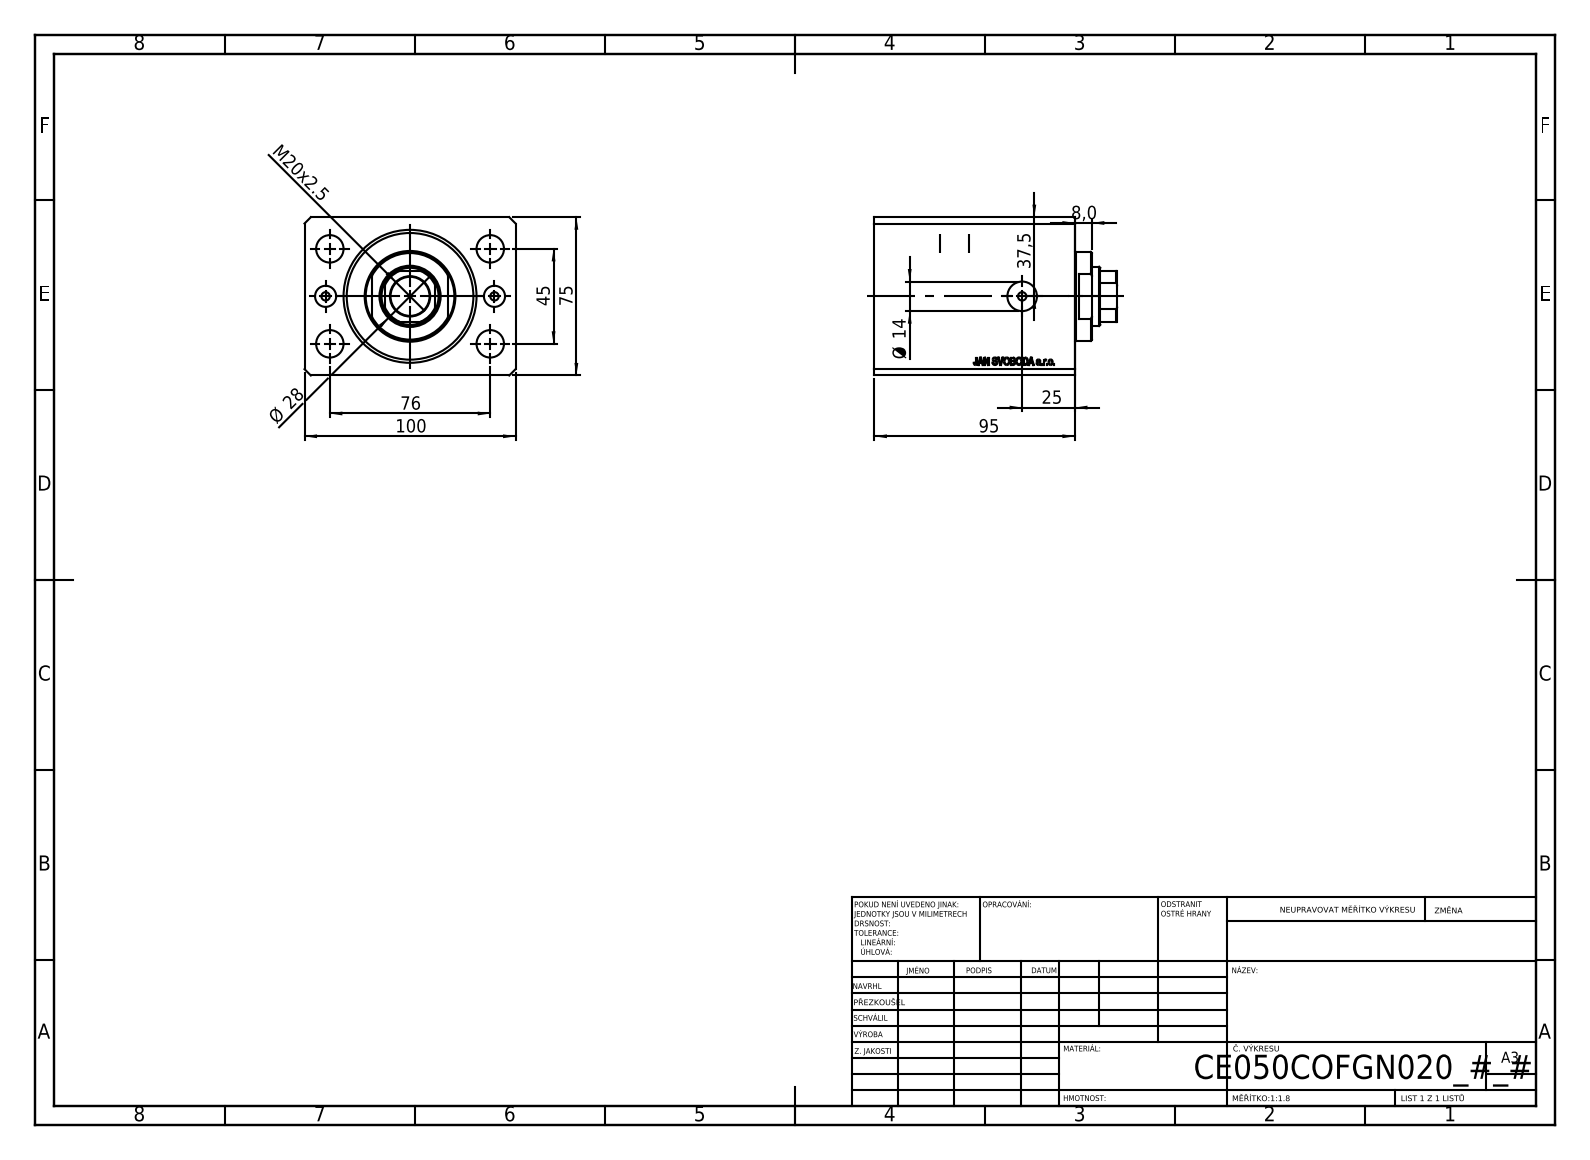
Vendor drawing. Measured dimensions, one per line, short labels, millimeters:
name: V250CE_C_VCP; V250CE_VC_C; V250CE_C_Body
written by: SolidWorks 2019 (CONFIG_CONTROL_DESIGN)
unit: mm
bodies: 3 solids, 864 faces (428 planar, 44 cylindrical, 392 other)
size: 115 × 100 × 75
volume: 637 792 mm³; area: 108 237 mm²
holes: 4× ⌀4, 4× ⌀13, 2× ⌀10, 2× ⌀14, 1× ⌀18.5, 1× ⌀28, 1× ⌀50, 1× ⌀63
bosses: 1× ⌀42
rounds: 1× R13.5
face distances: 75, 100, 20, 95, 11.9, 83.1, 63.1, 40, 55, 43.1
hole spacings: 22.59, 44.16, 81.18, 45, 40, 76, 88.32, 80
